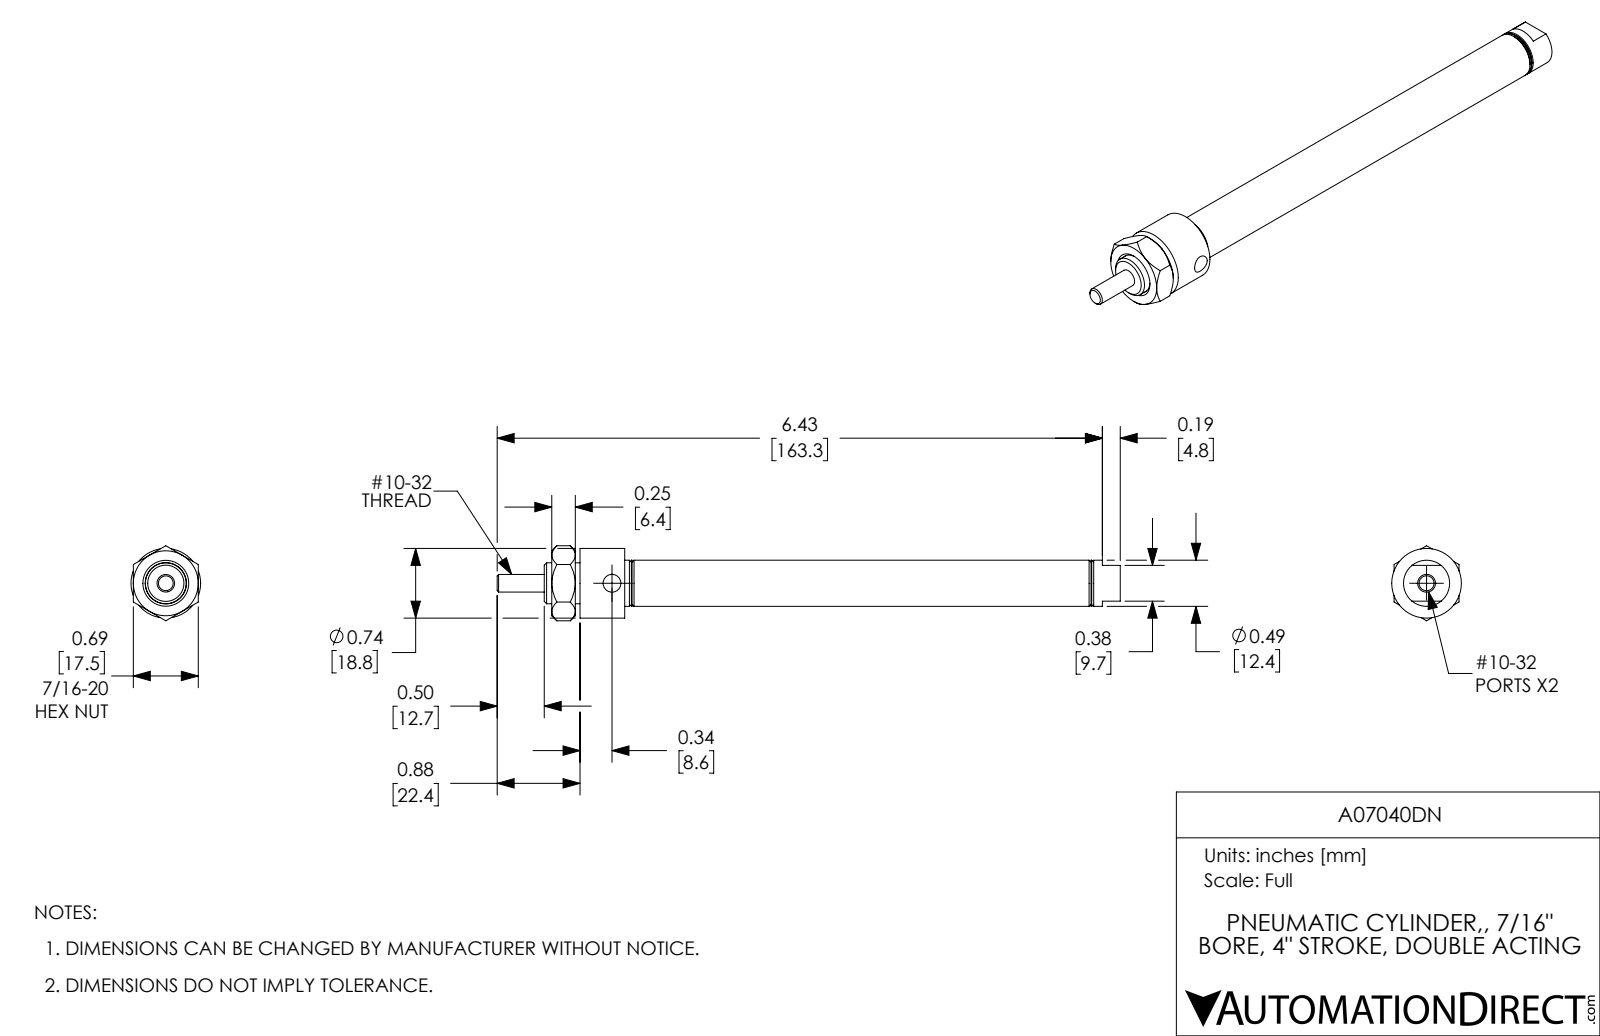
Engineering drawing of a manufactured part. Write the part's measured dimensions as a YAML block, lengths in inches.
part_name: "A07040DN_Mounting Nut_D-154; A07040DN-Rod; A07040DN; A07040DN-MainBody"
step_written_by: "SolidWorks 2017 (AUTOMOTIVE_DESIGN)"
units: inches
bodies: {solids: 3, faces: 92, planar: 28, cylindrical: 32, other: 32}
overall_size: [6.62, 0.797, 0.74]
volume: 0.809
surface_area: 23.8
round_holes:
  - {diameter: 0.159, count: 2}
  - {diameter: 0.19, count: 2}
  - {diameter: 0.187, count: 1}
  - {diameter: 0.437, count: 1}
round_bosses_or_shafts:
  - {diameter: 0.74, count: 1}
  - {diameter: 0.49, count: 1}
  - {diameter: 0.435, count: 1}
face_to_face_distances: [5.12, 0.62, 0.69, 4.645, 0.475, 0.05, 0.525, 5.42, 0.775, 0.3]
